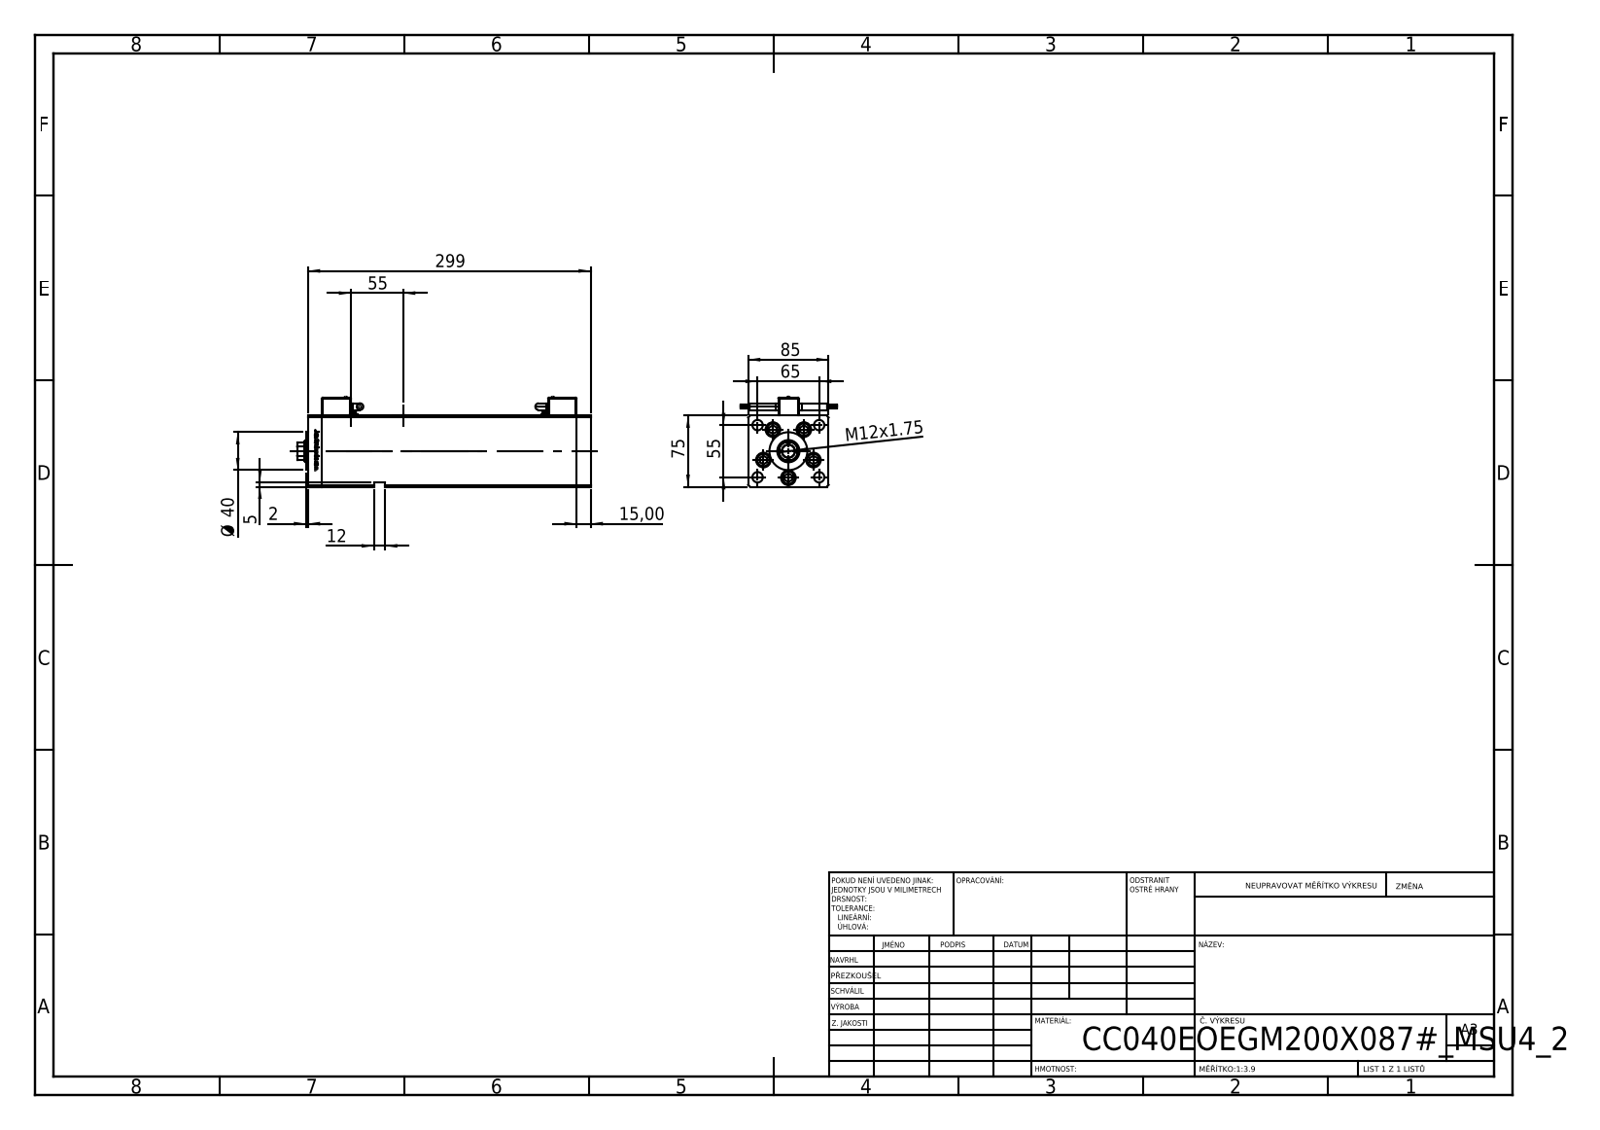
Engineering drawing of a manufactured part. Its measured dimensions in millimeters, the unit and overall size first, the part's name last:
Units: millimetres
Overall size (bounding box): 310 × 101.6 × 95.1
Round holes (diameter × count): ⌀11 ×9, ⌀15.5 ×5, ⌀10.5 ×4, ⌀16.5 ×4, ⌀2 ×2, ⌀3.6 ×2, ⌀5 ×2, ⌀7 ×2, ⌀13.16 ×2, ⌀13.5 ×1, ⌀22 ×1, ⌀23.5 ×1
Round bosses / shafts (diameter × count): ⌀0.85 ×8, ⌀14.5 ×5, ⌀8 ×5, ⌀7 ×4, ⌀6 ×2, ⌀3.5 ×2, ⌀2.5 ×2, ⌀40 ×1
Partial cylindrical surfaces — rounded edges, fillets, slot ends (radius × count): R1 ×24, R4 ×4, R0.93 ×2, R10.5 ×1
Main face-to-face distances: 85, 75, 15, 268.5, 283.5, 68.5, 10.5, 6.5, 4, 298.5
Hole centre spacings: 28, 42.57, 55, 65, 85.15, 8.25, 16.86, 19.17
Volume: 1 643 000 mm³ · Surface area: 247 618 mm²
Bodies: 16 solids, 1418 faces (553 planar, 255 cylindrical, 610 other)
Part name (STEP PRODUCT): V220C_E MIDDLE; ALLEN BOLT; V220C BACK_E; V220C_FRONT_E (+2 more)
STEP written by: SolidWorks 2019 (CONFIG_CONTROL_DESIGN)
